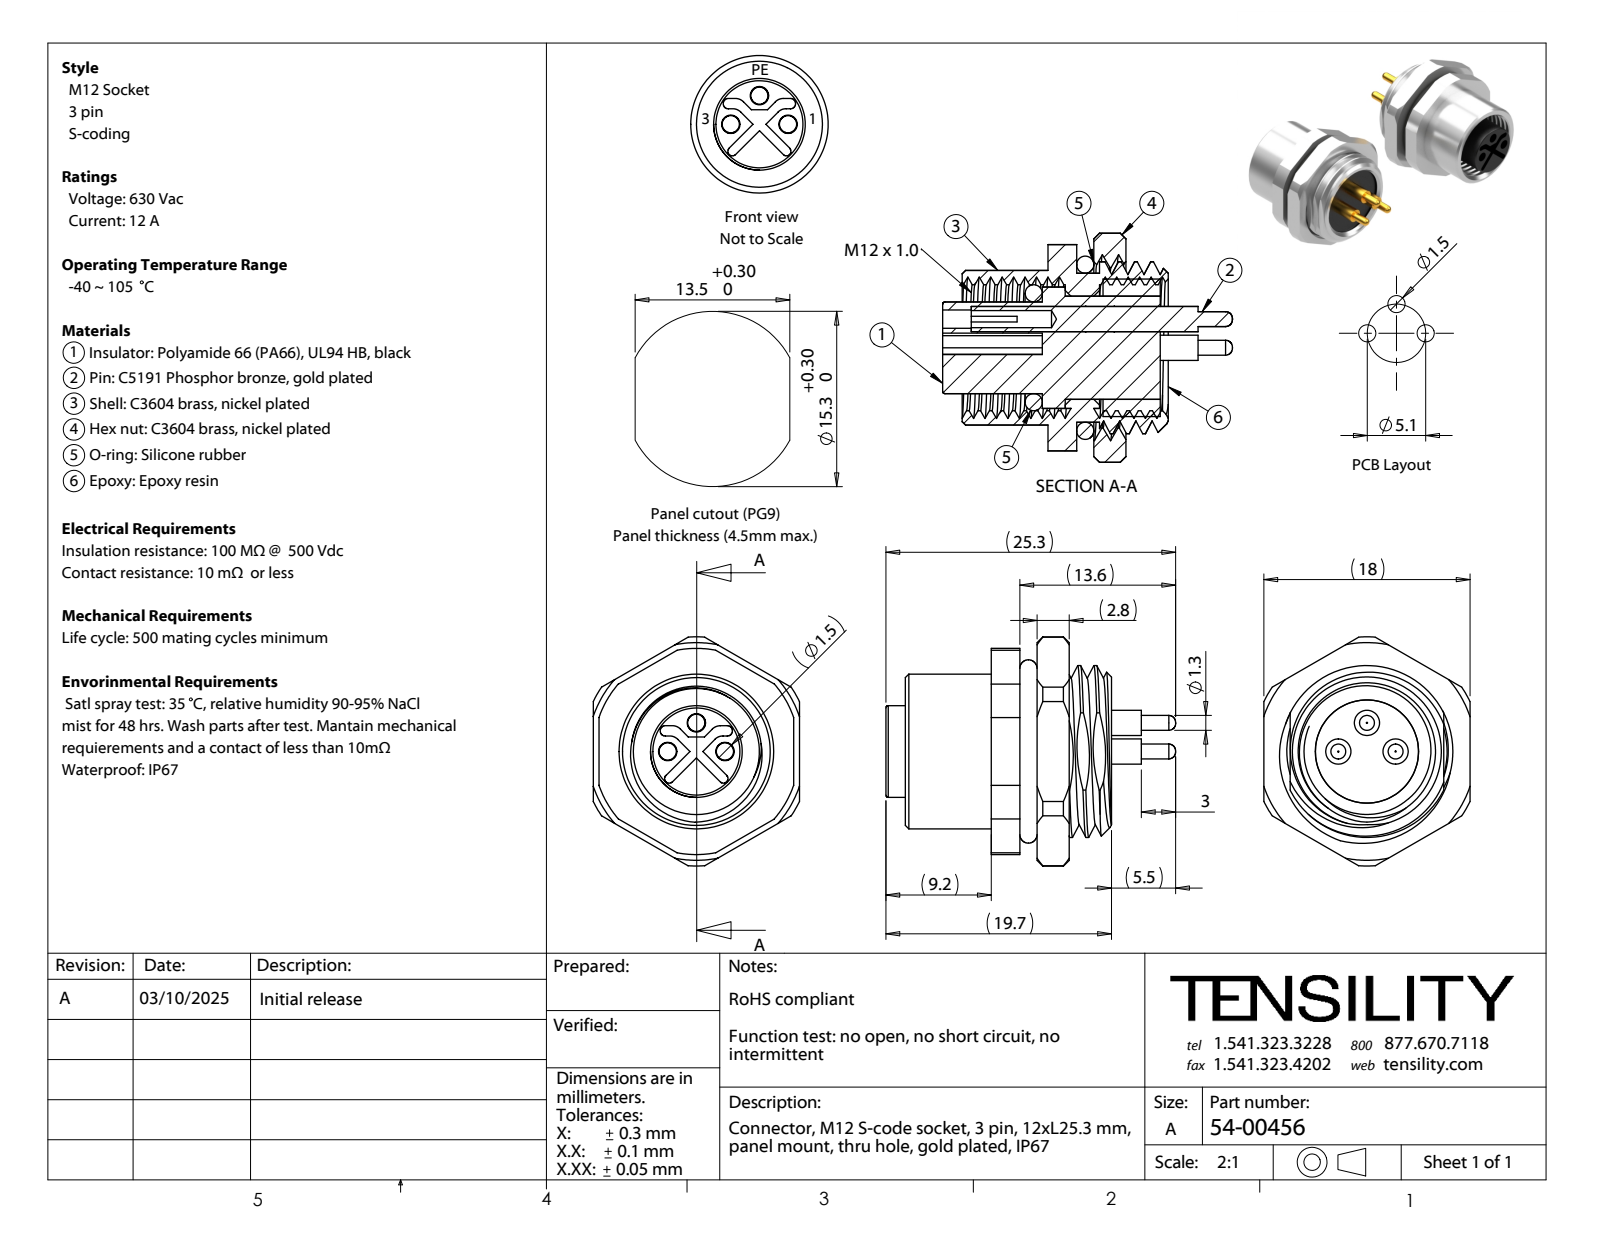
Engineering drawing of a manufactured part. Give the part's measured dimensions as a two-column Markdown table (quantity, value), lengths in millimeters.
| quantity | value |
| --- | --- |
| part name | 54-00456-05; 54-00456; 54-00456-02; 54-00456-01 (+3 more) |
| STEP written by | SolidWorks 2021 (CONFIG_CONTROL_DESIGN) |
| units | millimeters |
| bodies | 9 solids, 295 faces (92 planar, 127 cylindrical, 76 other) |
| overall size | 25.3 × 20 × 18 |
| volume | 2 768 mm³ |
| surface area | 5 698 mm² |
| round holes (diameter × count) | 1.5 × 3, 1.6 × 3, 9 × 1, 11 × 1, 14 × 1 |
| round bosses / shafts (diameter × count) | 2.2 × 3, 1.3 × 3, 13.5 × 1, 13 × 1, 12 × 1, 10.6 × 1, 8 × 1 |
| partial cylindrical surfaces (radius × count) | 1 × 4, 0.4 × 2, 0.45 × 2, 7.5 × 1, 9 × 1, 10 × 1 |
| main face-to-face distances | 0.5, 3, 7.3, 2.5, 2.3, 0.8, 5.3, 2, 1.5, 9.8 |
| hole center spacings | 2.5, 3.54, 5 |
